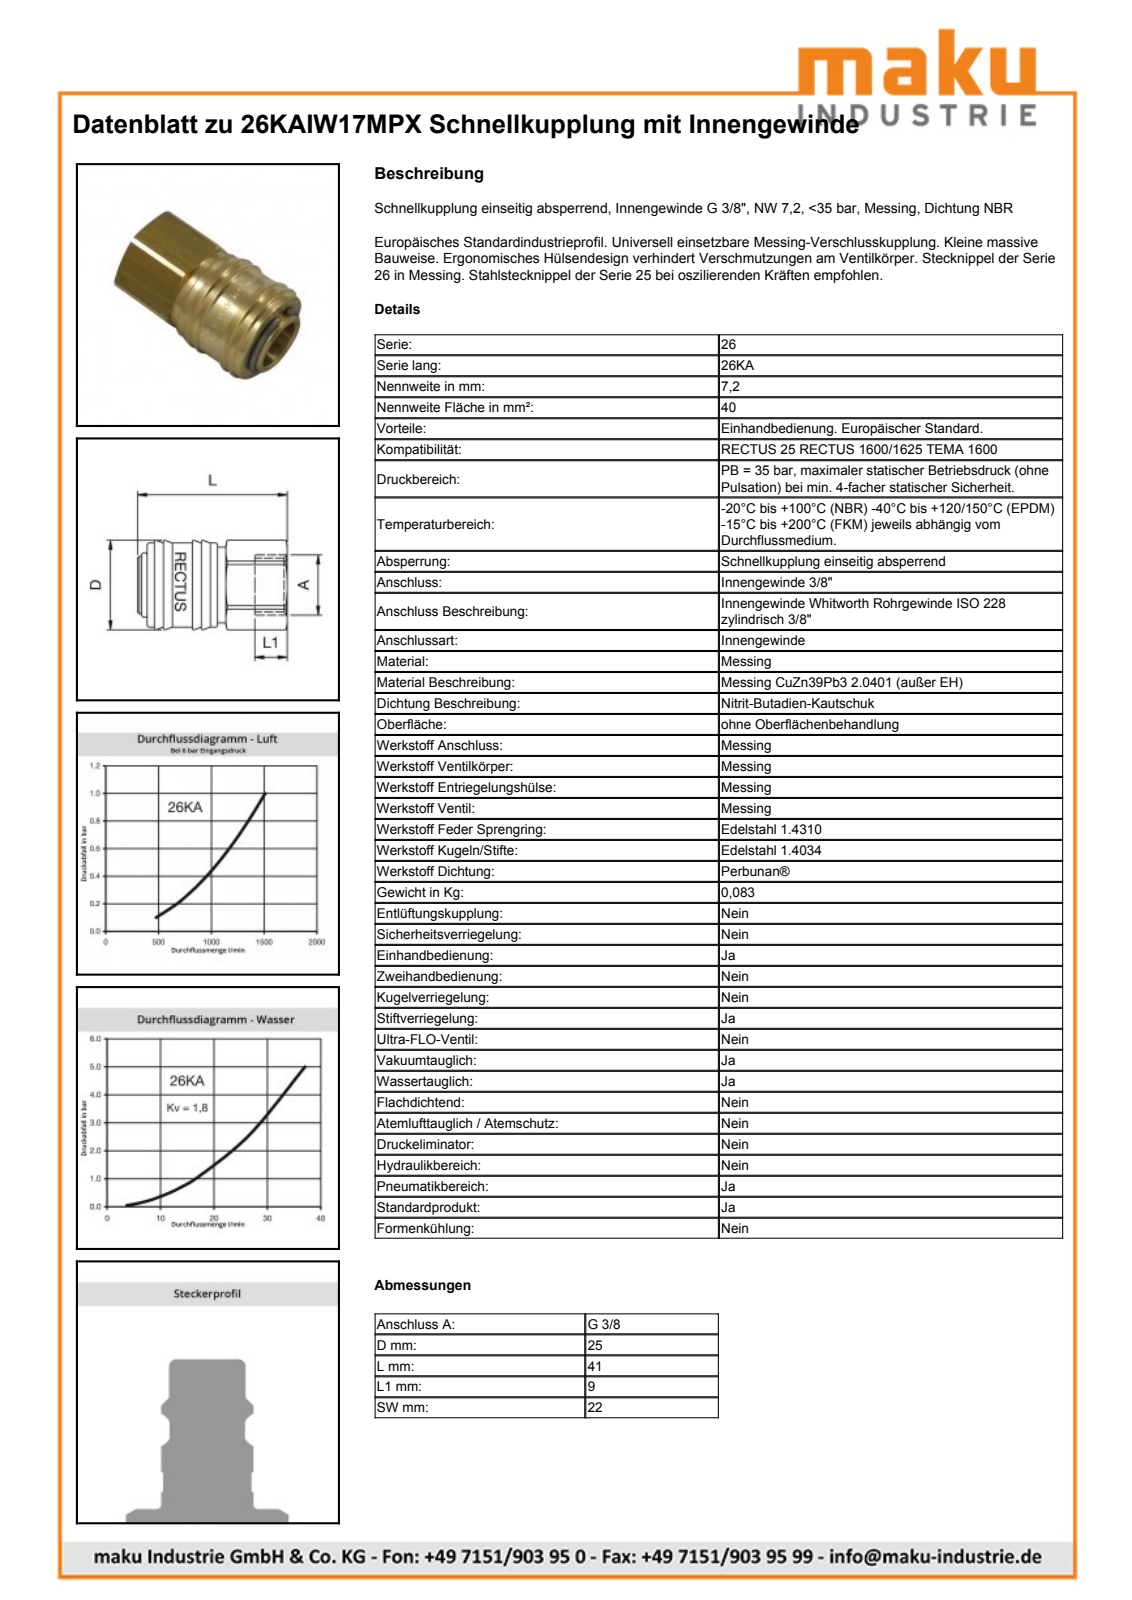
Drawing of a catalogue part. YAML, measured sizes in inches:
part_name: "D111716"
step_written_by: "Autodesk Inventor 2013 (AUTOMOTIVE_DESIGN)"
units: inches
bodies: {solids: 2, faces: 461, planar: 175, cylindrical: 62, other: 224}
overall_size: [1.618, 0.976, 0.976]
volume: 0.815
surface_area: 12.22
round_holes:
  - {diameter: 0.402, count: 1}
  - {diameter: 0.589, count: 1}
  - {diameter: 0.608, count: 1}
  - {diameter: 0.634, count: 1}
  - {diameter: 0.669, count: 1}
  - {diameter: 0.831, count: 1}
round_bosses_or_shafts:
  - {diameter: 0.917, count: 1}
  - {diameter: 0.827, count: 1}
  - {diameter: 0.709, count: 1}
  - {diameter: 0.656, count: 1}
  - {diameter: 0.628, count: 1}
  - {diameter: 0.602, count: 1}
partial_cylinders:
  - {radius: 0.455, count: 1}
  - {radius: 0.488, count: 1}
face_to_face_distances: [0.866, 0.104, 1.264, 1.159, 1.618, 1.514, 0.354, 0.827, 0.722, 0.437]
